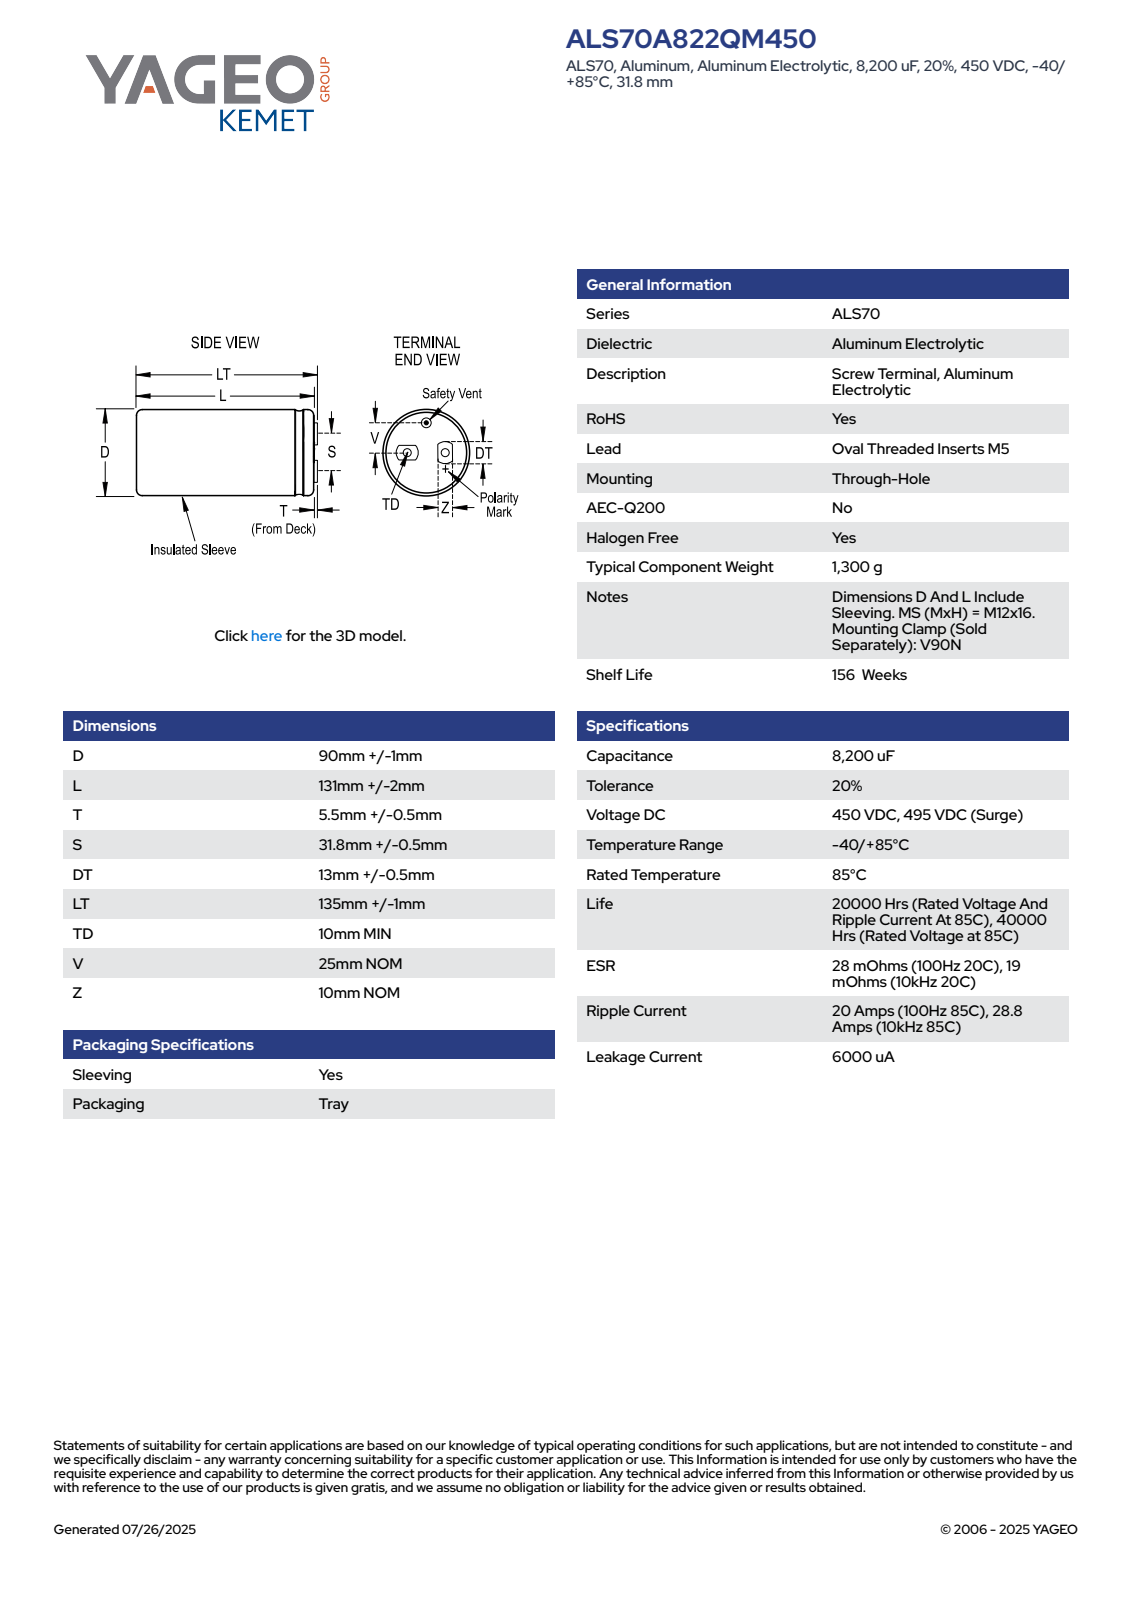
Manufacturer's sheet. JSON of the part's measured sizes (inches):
{"part_name": "CARC_KALSO_90X131_D91L133T6S31.8LT136.00V25.000", "step_written_by": "SolidWorks 2014 (AUTOMOTIVE_DESIGN)", "units": "inches", "bodies": {"solids": 1, "faces": 109, "planar": 40, "cylindrical": 30, "other": 39}, "overall_size": [5.433, 3.583, 3.583], "volume_in3": 52.36, "surface_area_in2": 81.08, "round_holes": [[0.197, 2], [0.079, 1], [3.425, 1]], "round_bosses_or_shafts": [[0.669, 2], [3.583, 1], [0.118, 1]], "partial_cylinders_radius": [[0.315, 4], [1.791, 1]], "face_to_face_distances": [5.197, 5.217, 0.02, 5.433, 0.236, 0.217, 0.394, 5.039, 0.157, 0.177], "hole_center_spacings": [0.626, 1.167, 0.984, 1.252]}
